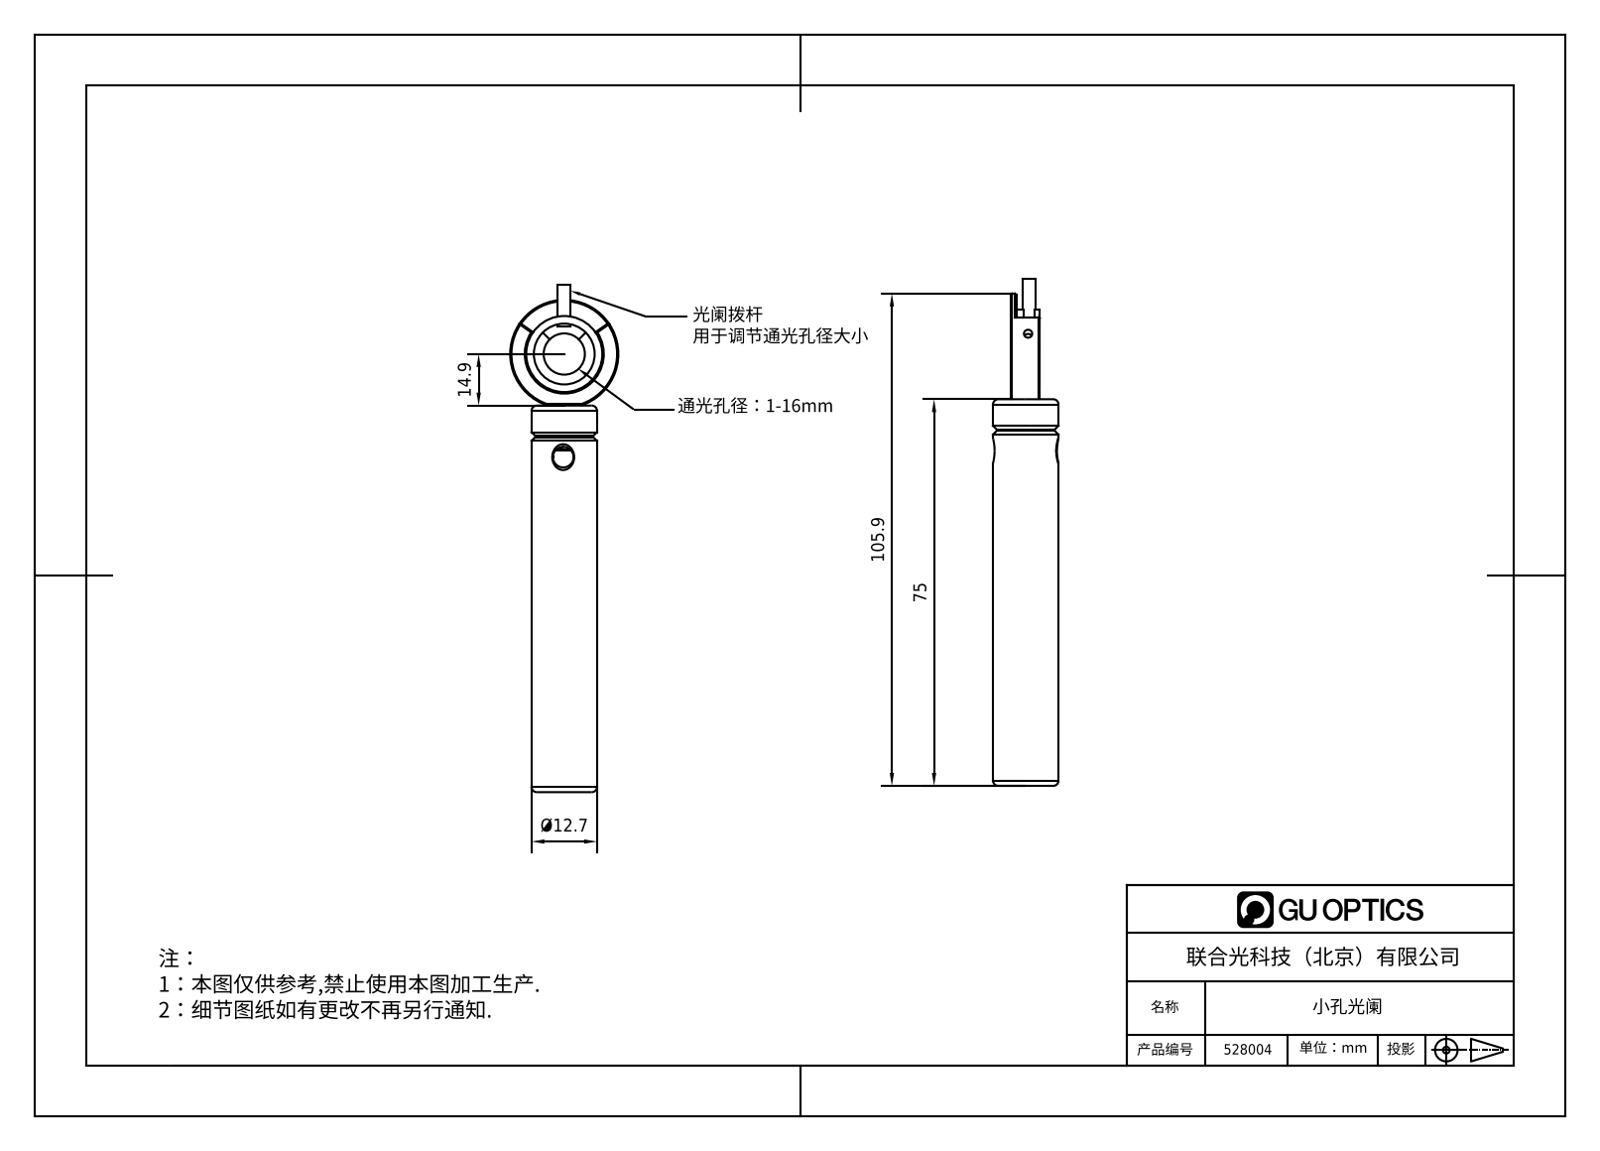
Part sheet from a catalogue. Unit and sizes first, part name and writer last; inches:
Units: inches
Overall size (bounding box): 4.089 × 1.057 × 0.5
Round holes (diameter × count): ⌀0.13 ×1, ⌀0.157 ×1, ⌀0.197 ×1, ⌀0.472 ×1, ⌀0.689 ×1, ⌀0.78 ×1
Round bosses / shafts (diameter × count): ⌀1.039 ×1, ⌀0.5 ×1, ⌀0.157 ×1, ⌀0.059 ×1
Partial cylindrical surfaces — rounded edges, fillets, slot ends (radius × count): R0.315 ×1
Main face-to-face distances: 0.03, 0.197, 0.227, 0.22, 0.19, 2.953, 0.039, 0.157, 0.07, 0.151
Volume: 0.672 in³ · Surface area: 9.052 in²
Bodies: 4 solids, 65 faces (30 planar, 14 cylindrical, 21 other)
Part name (STEP PRODUCT): 528004
STEP written by: SolidWorks 2020 (CONFIG_CONTROL_DESIGN)
